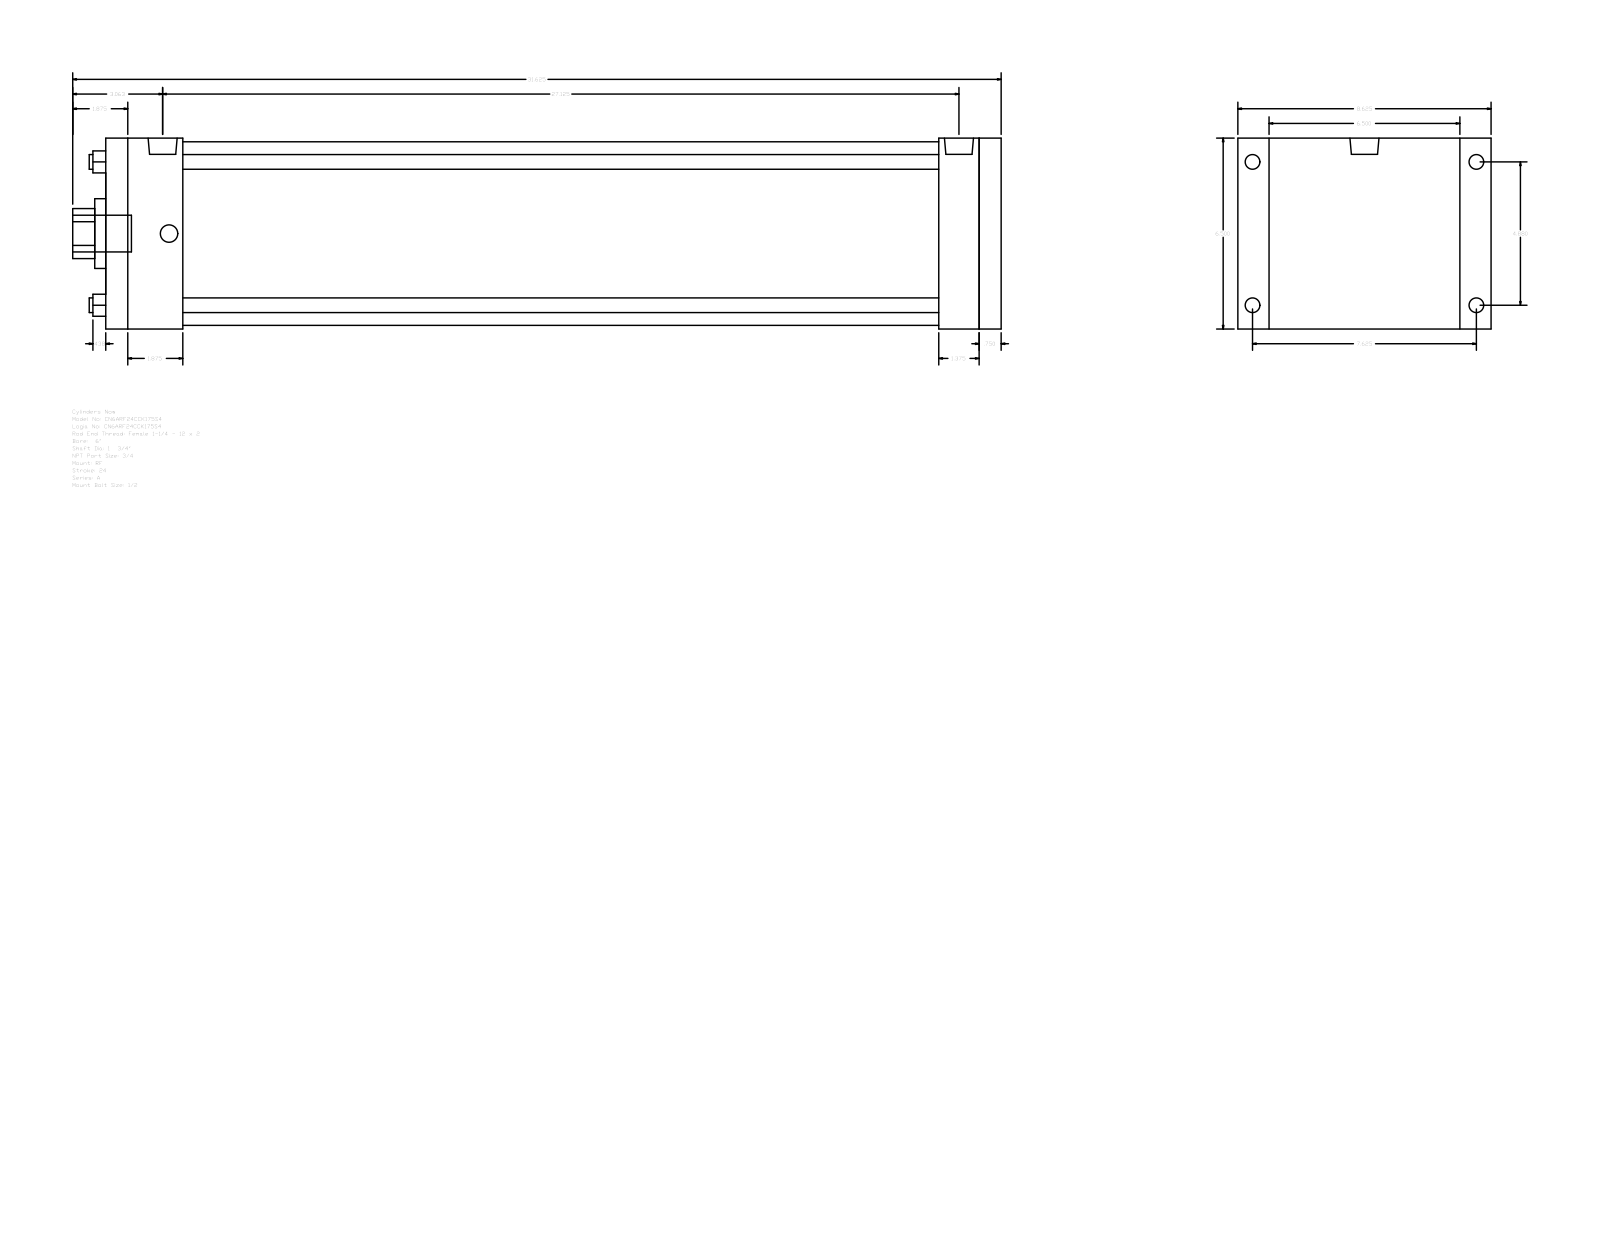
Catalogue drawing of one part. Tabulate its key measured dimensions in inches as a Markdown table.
| quantity | value |
| --- | --- |
| part name | A_RF__0600_1.75 |
| STEP written by | GSSL Pune (CONFIG_CONTROL_DESIGN) |
| units | inches |
| bodies | 0 solids, 92 faces (64 planar, 28 cylindrical, 0 other) |
| overall size | 31.625 × 8.625 × 6.5 |
| round holes (diameter × count) | 0.5 × 4, 1.75 × 1, 2.375 × 1, 6.25 × 1 |
| round bosses / shafts (diameter × count) | 0.594 × 4, 0.5 × 4, 0.989 × 2, 1.25 × 1 |
| partial cylindrical surfaces (radius × count) | 0.852 × 1 |
| main face-to-face distances | 6.5, 30.5, 29.75, 0.75, 2.625, 27.125, 27.875, 28.375, 25.75, 1.375 |
| hole center spacings | 3.451, 4.88, 6.902 |
